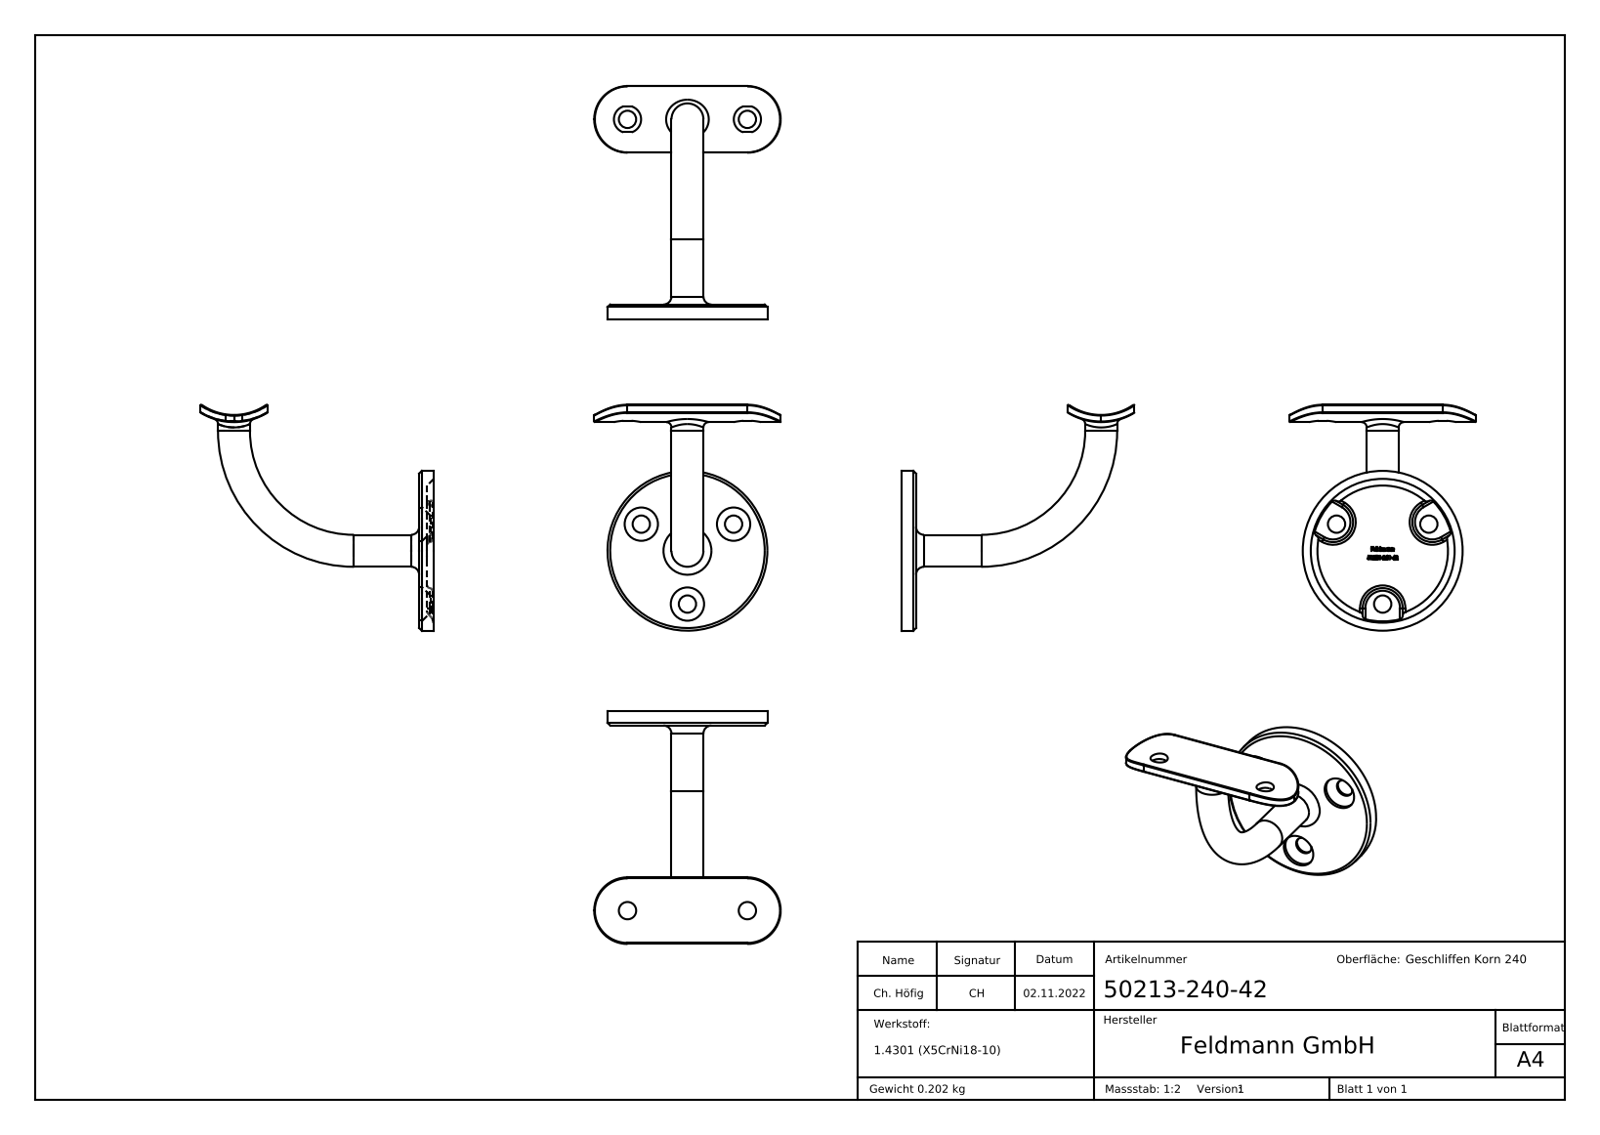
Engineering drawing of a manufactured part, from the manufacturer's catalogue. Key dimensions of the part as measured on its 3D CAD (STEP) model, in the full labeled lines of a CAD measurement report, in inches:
Part name (STEP PRODUCT): 50213-240-42
STEP written by: SolidWorks 2018 (CONFIG_CONTROL_DESIGN)
Units: inches
Bodies: 1 solid, 323 faces (158 planar, 37 cylindrical, 128 other)
Overall size (bounding box): 3.445 × 3.34 × 2.756
Volume: 1.561 in³ · Surface area: 22.02 in²
Round holes (diameter × count): ⌀0.256 ×5, ⌀0.492 ×3, ⌀0.402 ×2
Round bosses / shafts (diameter × count): ⌀0.472 ×2, ⌀2.362 ×1
Partial cylindrical surfaces — rounded edges, fillets, slot ends (radius × count): R0.039 ×12, R0.01 ×4, R0.492 ×2, R0.835 ×1, R0.941 ×1
Main face-to-face distances: 0.118, 0.098, 0.217, 0.02, 0.079, 0.197, 3.445, 3.425, 3.346, 3.228
Hole centre spacings: 1.364, 1.772
